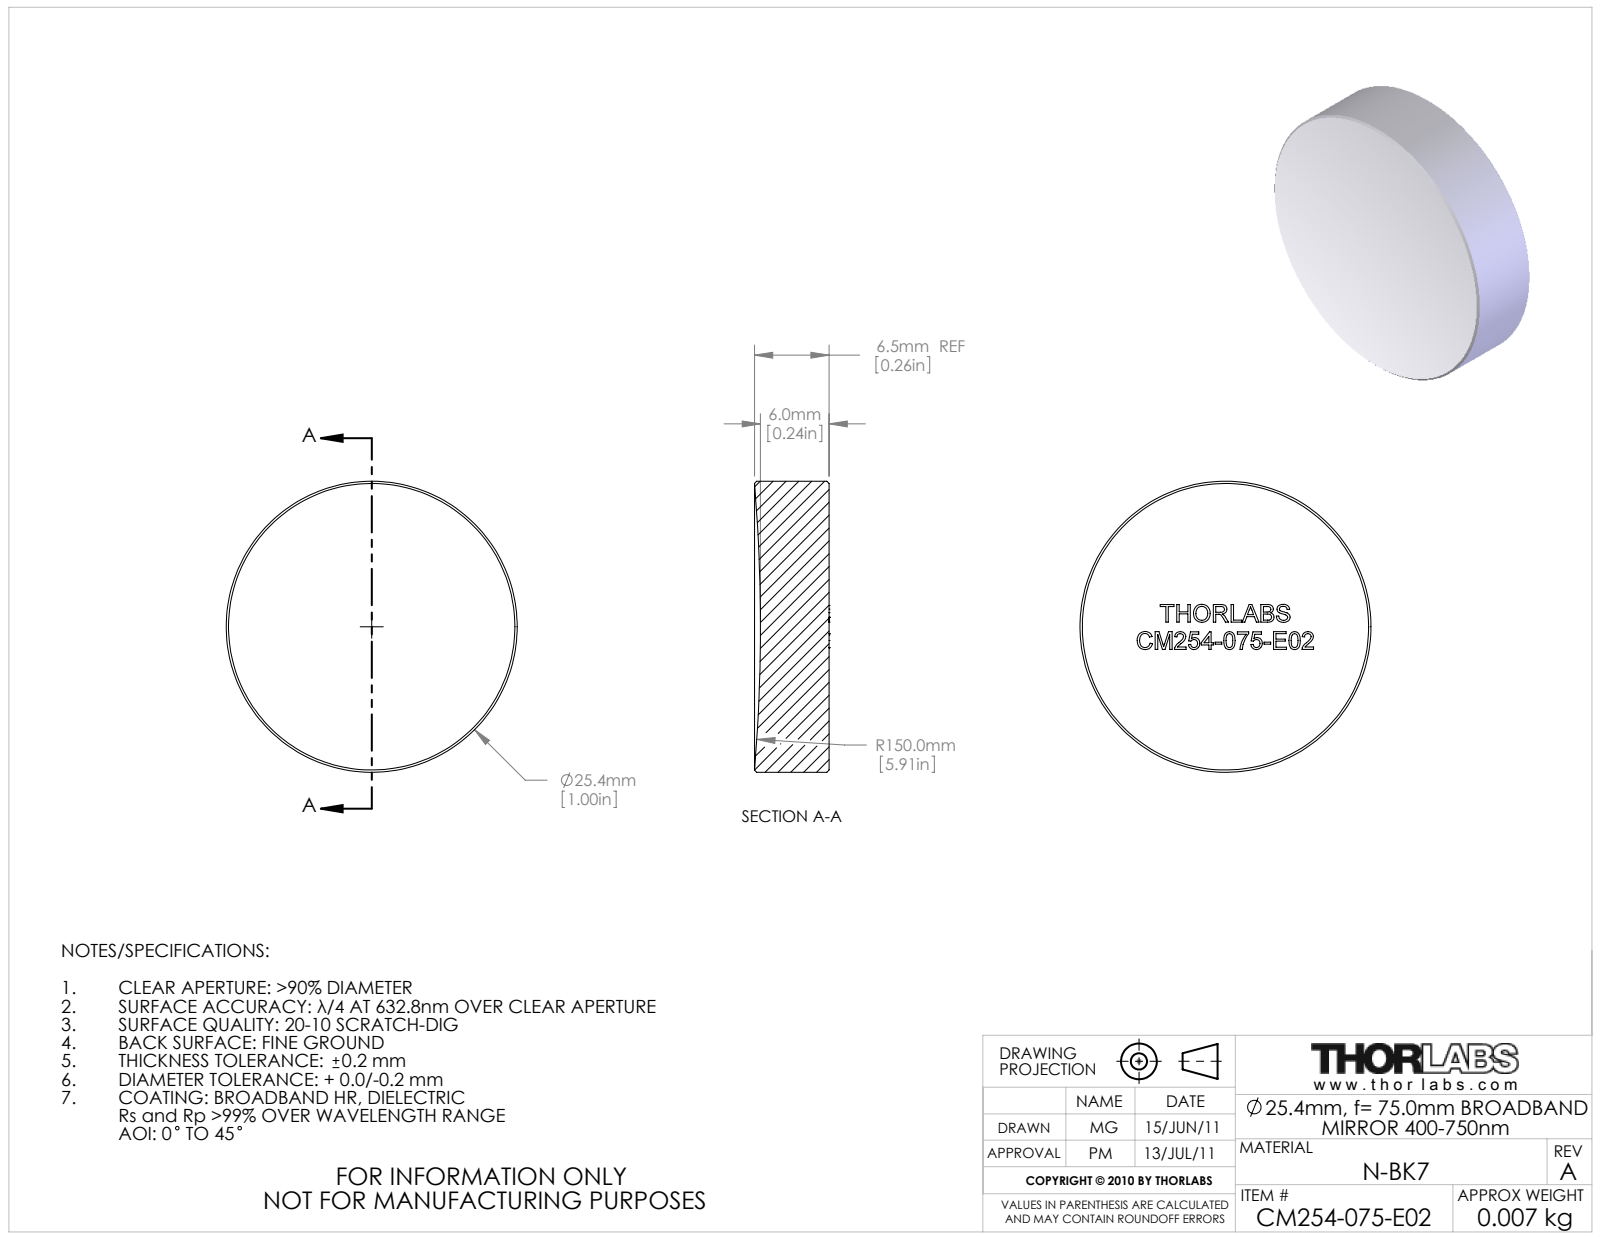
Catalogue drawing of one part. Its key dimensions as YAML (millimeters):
part_name: "22628-E0W"
step_written_by: "SolidWorks 2011 (AUTOMOTIVE_DESIGN)"
units: millimeters
bodies: {solids: 0, faces: 39, planar: 30, cylindrical: 2, other: 7}
overall_size: [25.4, 25.4, 6.52]
round_bosses_or_shafts:
  - {diameter: 25.4, count: 1}
